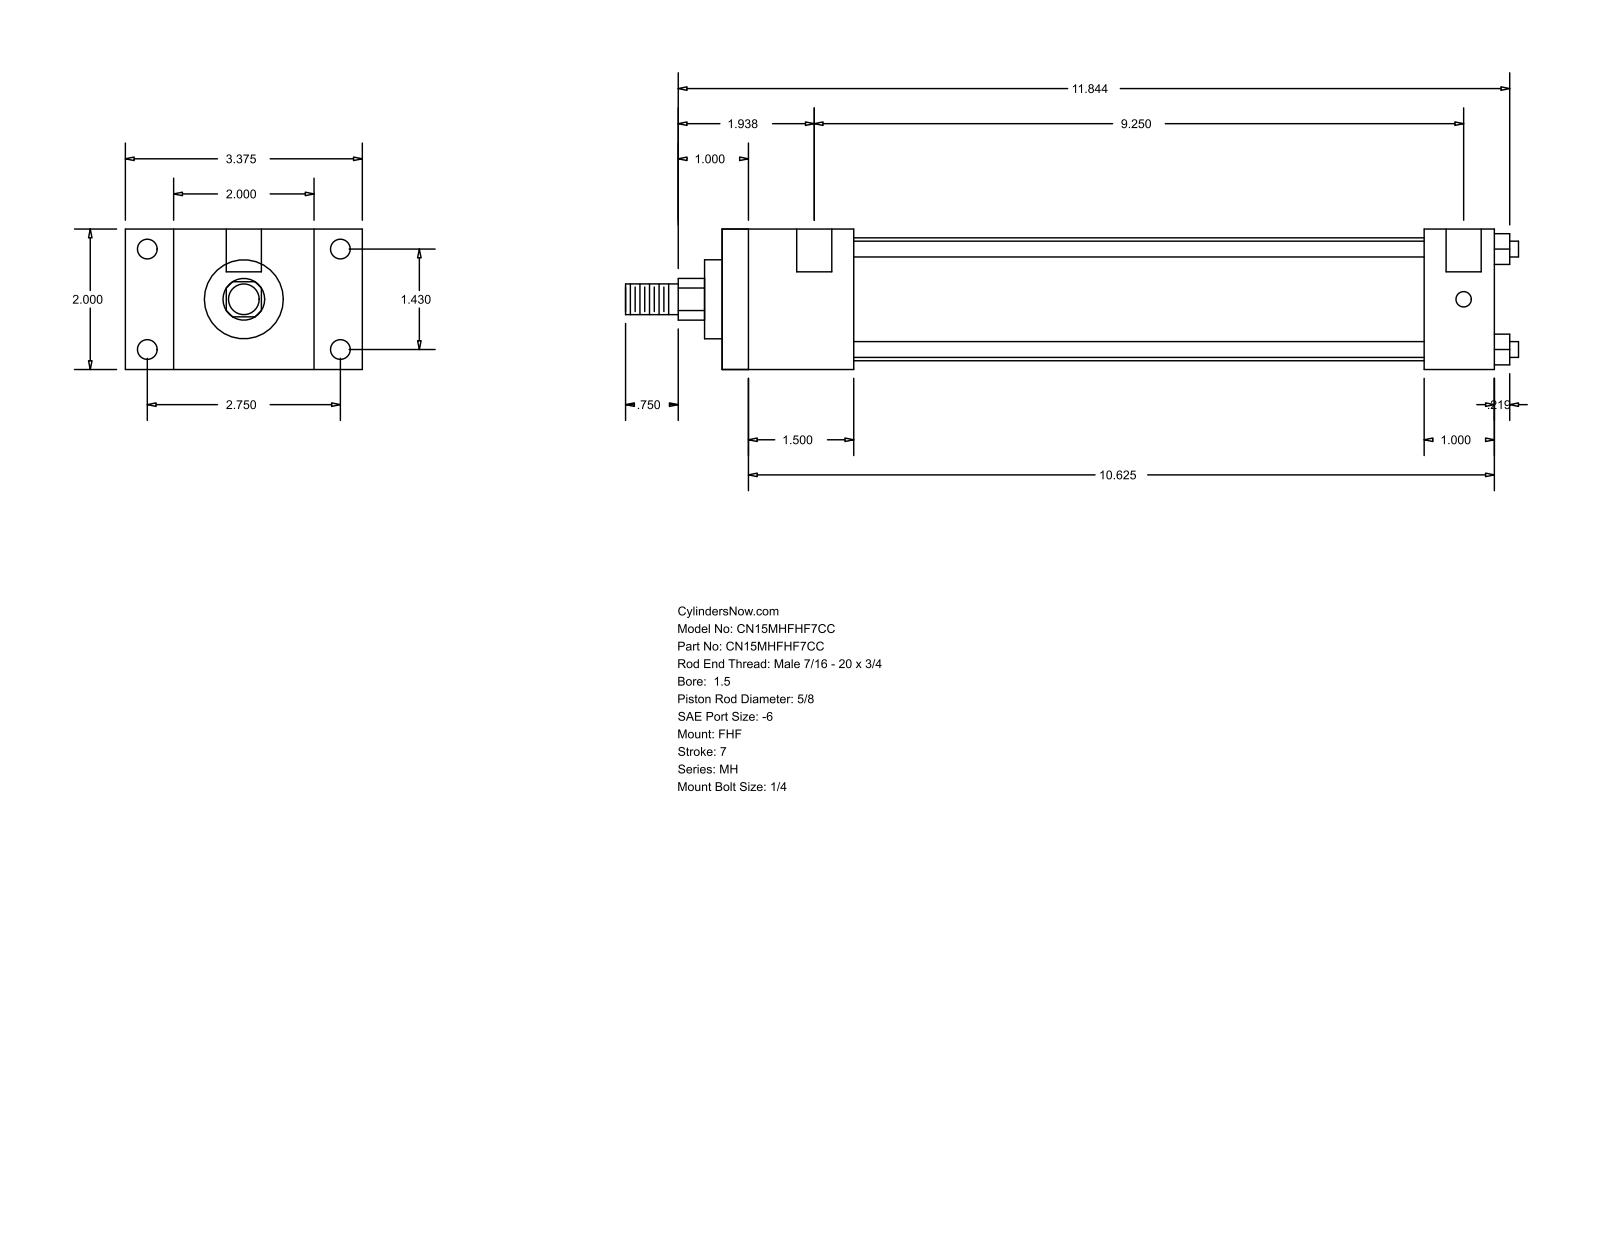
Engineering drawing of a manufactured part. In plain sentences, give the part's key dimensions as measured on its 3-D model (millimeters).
The part is named "MH_FHF__0150_0.625". Its 3-D file was written by "GSSL Pune (CONFIG_CONTROL_DESIGN)". It is 0 solids with 88 faces: 60 planar, 28 cylindrical and 0 other. Overall it measures 323.06 by 85.72 by 50.8 millimeters. Round holes: 4 of diameter 5.56, 4 of diameter 7.14, 2 of diameter 12.7. Round bosses or shafts: 4 of diameter 5.71, 1 of diameter 44.45, 1 of diameter 28.57, 1 of diameter 15.88, 1 of diameter 11.11. Partial cylindrical surfaces (rounded edges, fillets, slot ends): 1 of radius 7.54. The main face-to-face distances are 50.8, 17.46, 68.26, 47.62, 85.72, 279.39, 231.77, 254, 206.38, 25.39. The hole center spacings are 36.32, 69.84, 78.72, 238.12, 3.17, 234.95.
